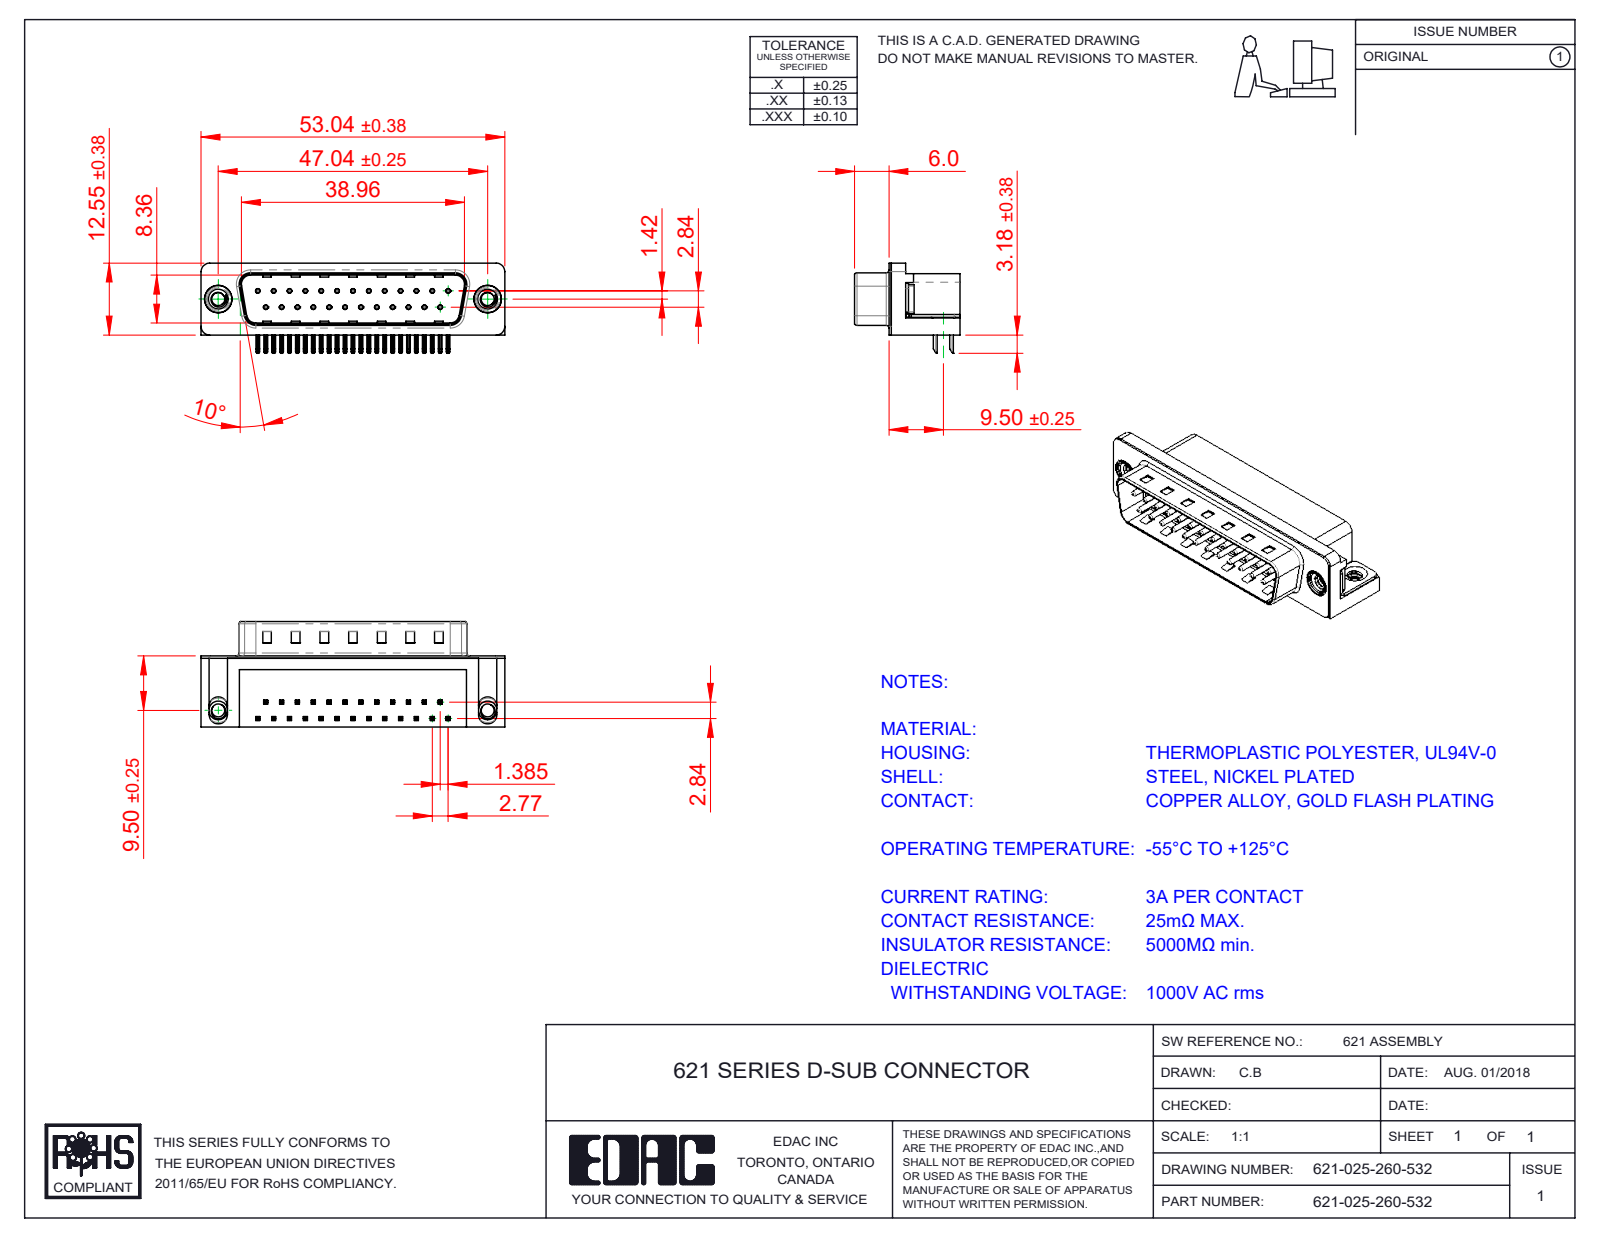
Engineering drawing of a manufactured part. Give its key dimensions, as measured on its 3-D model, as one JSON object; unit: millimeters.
{"part_name": "621 Contact Top; 621 Contact Bottom; 621-025-260-532; 621 Shell_25 Socket (+3 more)", "step_written_by": "SolidWorks 2016 (CONFIG_CONTROL_DESIGN)", "units": "millimeters", "bodies": {"solids": 31, "faces": 2303, "planar": 1437, "cylindrical": 667, "other": 199}, "overall_size": [53.04, 18.4, 16.25], "volume_mm3": 6348, "surface_area_mm2": 7689, "round_holes": [[0.35, 25], [0.8, 25], [2.26, 2], [4, 2], [4.8, 2], [5, 2]], "round_bosses_or_shafts": [[0.75, 25], [4.9, 2], [4.75, 2], [3.9, 2]], "partial_cylinders_radius": [[0.25, 108], [0.12, 50], [1, 16], [0.5, 14], [1.6, 8], [1.5, 7], [0.32, 4], [0.9, 4]], "face_to_face_distances": [0.4, 12, 10.35, 2.1, 8.76, 10.46, 10.86, 1.7, 12.4, 9], "hole_center_spacings": [3.16, 2.77, 5.54, 8.31, 11.08, 13.85, 16.62, 5.03]}
